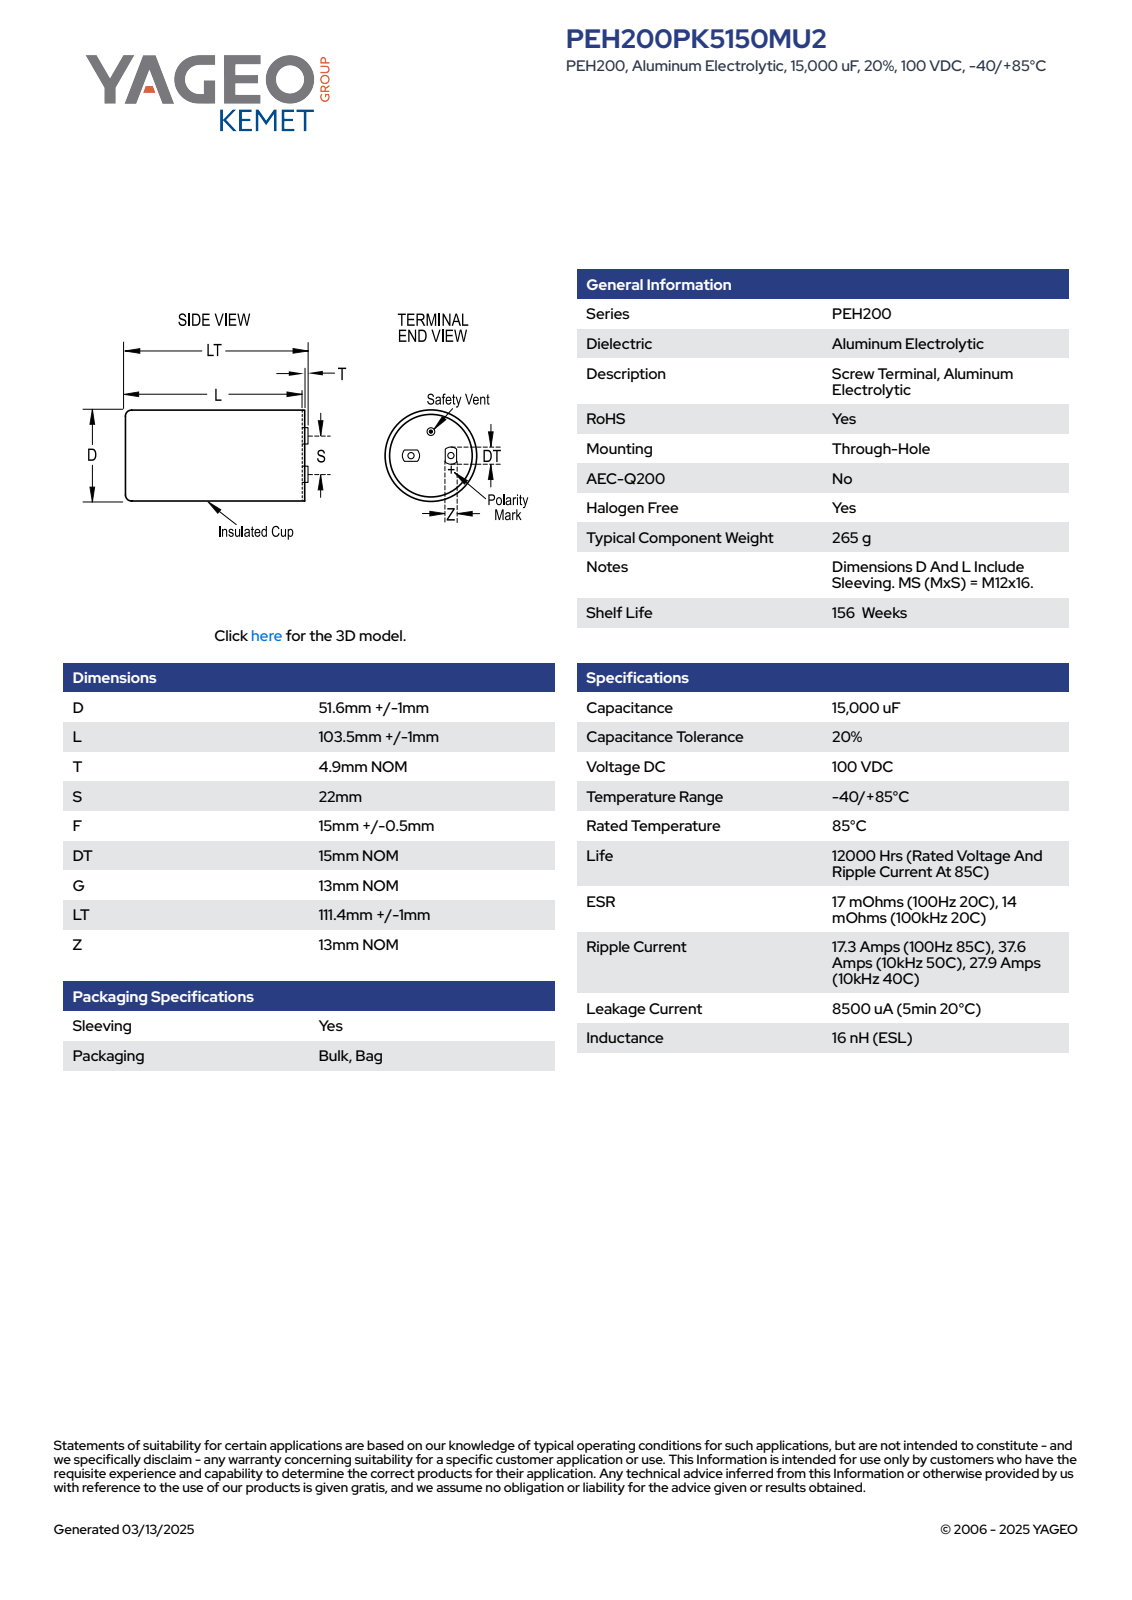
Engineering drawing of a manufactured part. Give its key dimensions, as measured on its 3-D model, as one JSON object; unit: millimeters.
{"part_name": "Oval_Terminal_3; CARC_D52.6L104.5S22T4.9; Can_3", "step_written_by": "SolidWorks 2014 (AUTOMOTIVE_DESIGN)", "units": "millimeters", "bodies": {"solids": 3, "faces": 91, "planar": 38, "cylindrical": 21, "other": 32}, "overall_size": [112.4, 52.6, 52.6], "volume_mm3": 229860, "surface_area_mm2": 24162, "round_holes": [[4.02, 2], [50.6, 1]], "round_bosses_or_shafts": [[7.5, 2], [52.6, 1]], "partial_cylinders_radius": [[7.5, 2], [26.29, 1]], "face_to_face_distances": [104.5, 7.9, 112.4, 4.9, 3, 107.5, 13, 12.9, 8, 5], "hole_center_spacings": [11, 22]}
